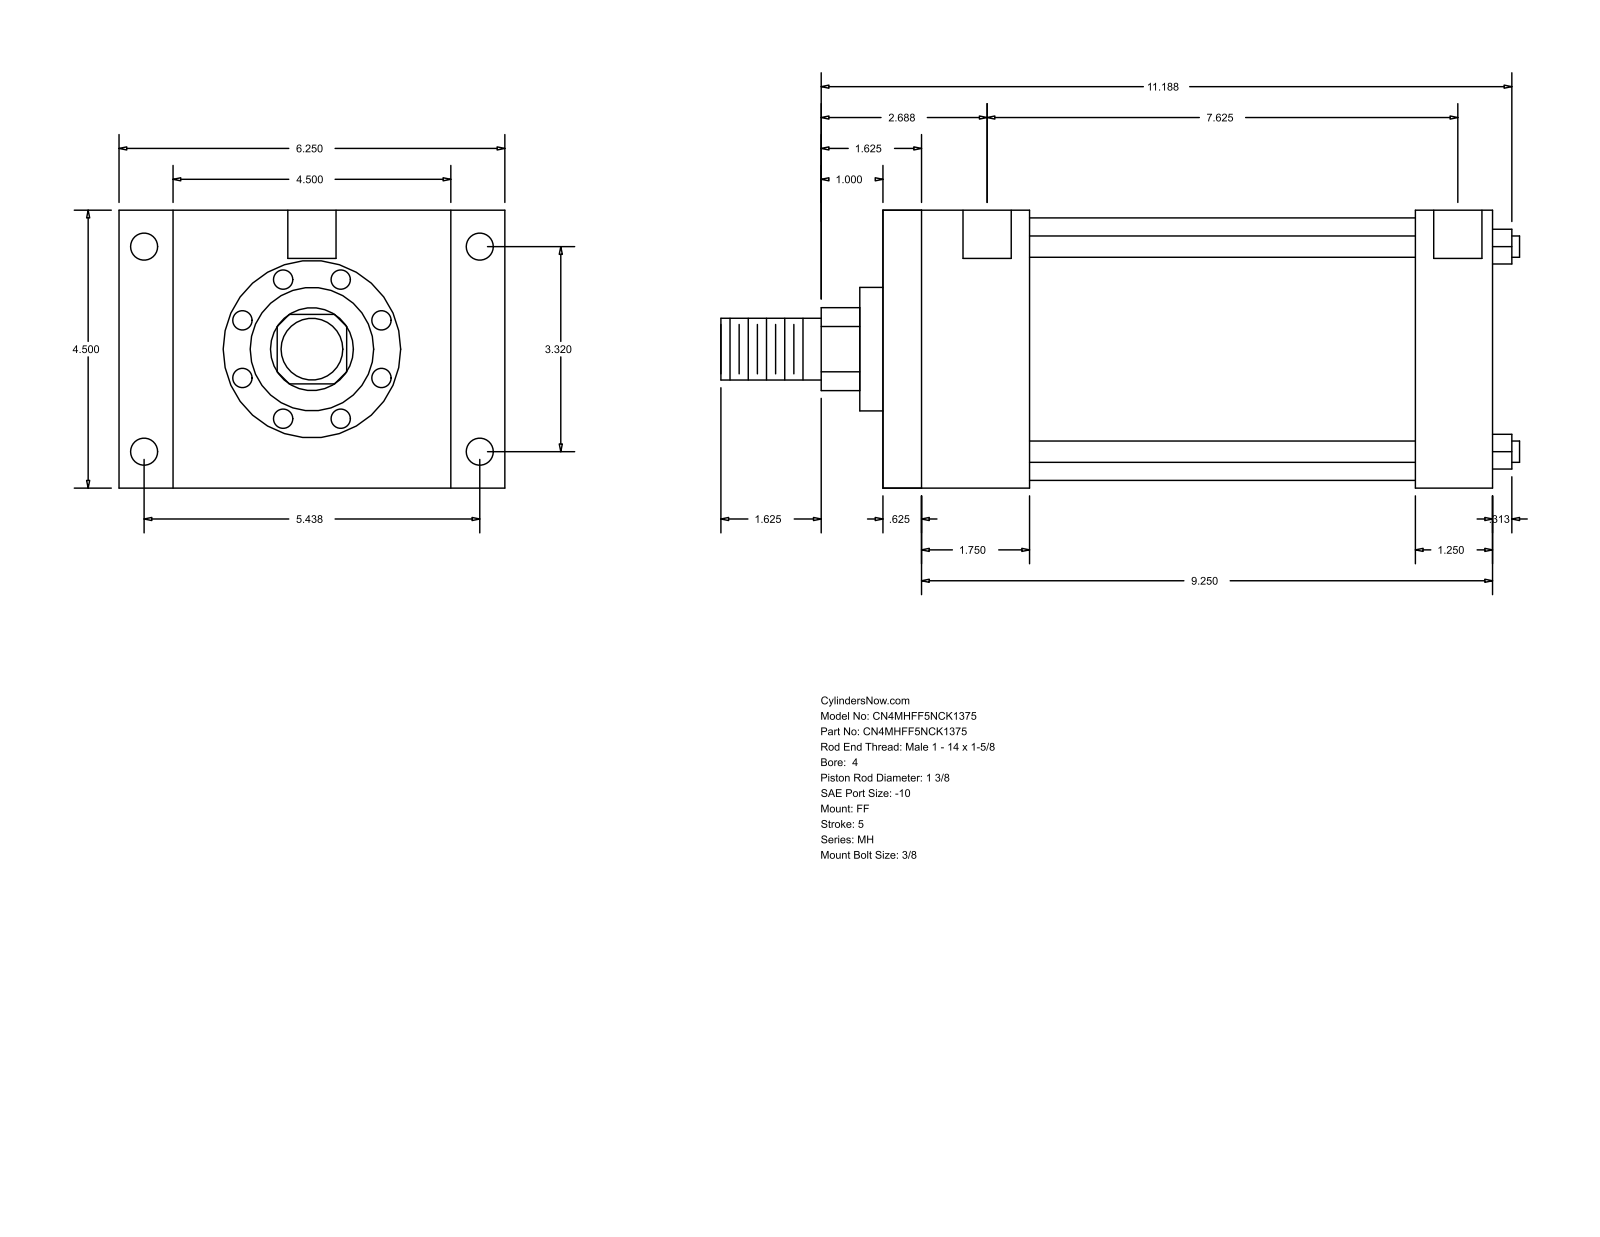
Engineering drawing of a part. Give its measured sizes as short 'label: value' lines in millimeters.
name: MH_FF__0400_1.375
written by: GSSL Pune (CONFIG_CONTROL_DESIGN)
unit: mm
bodies: 0 solids, 92 faces (64 planar, 28 cylindrical, 0 other)
size: 328.61 × 158.75 × 114.3
holes: 4× ⌀8.73, 4× ⌀11.13, 2× ⌀19.84
bosses: 4× ⌀8.76, 1× ⌀107.95, 1× ⌀50.8, 1× ⌀34.92, 1× ⌀25.4
rounds: 1× R17.06
face distances: 114.3, 250.83, 15.87, 234.96, 60.32, 44.45, 190.51, 219.07, 203.2, 158.75
hole spacings: 84.32, 138.12, 161.82, 196.85, 1.58, 1.59, 193.68, 195.26
